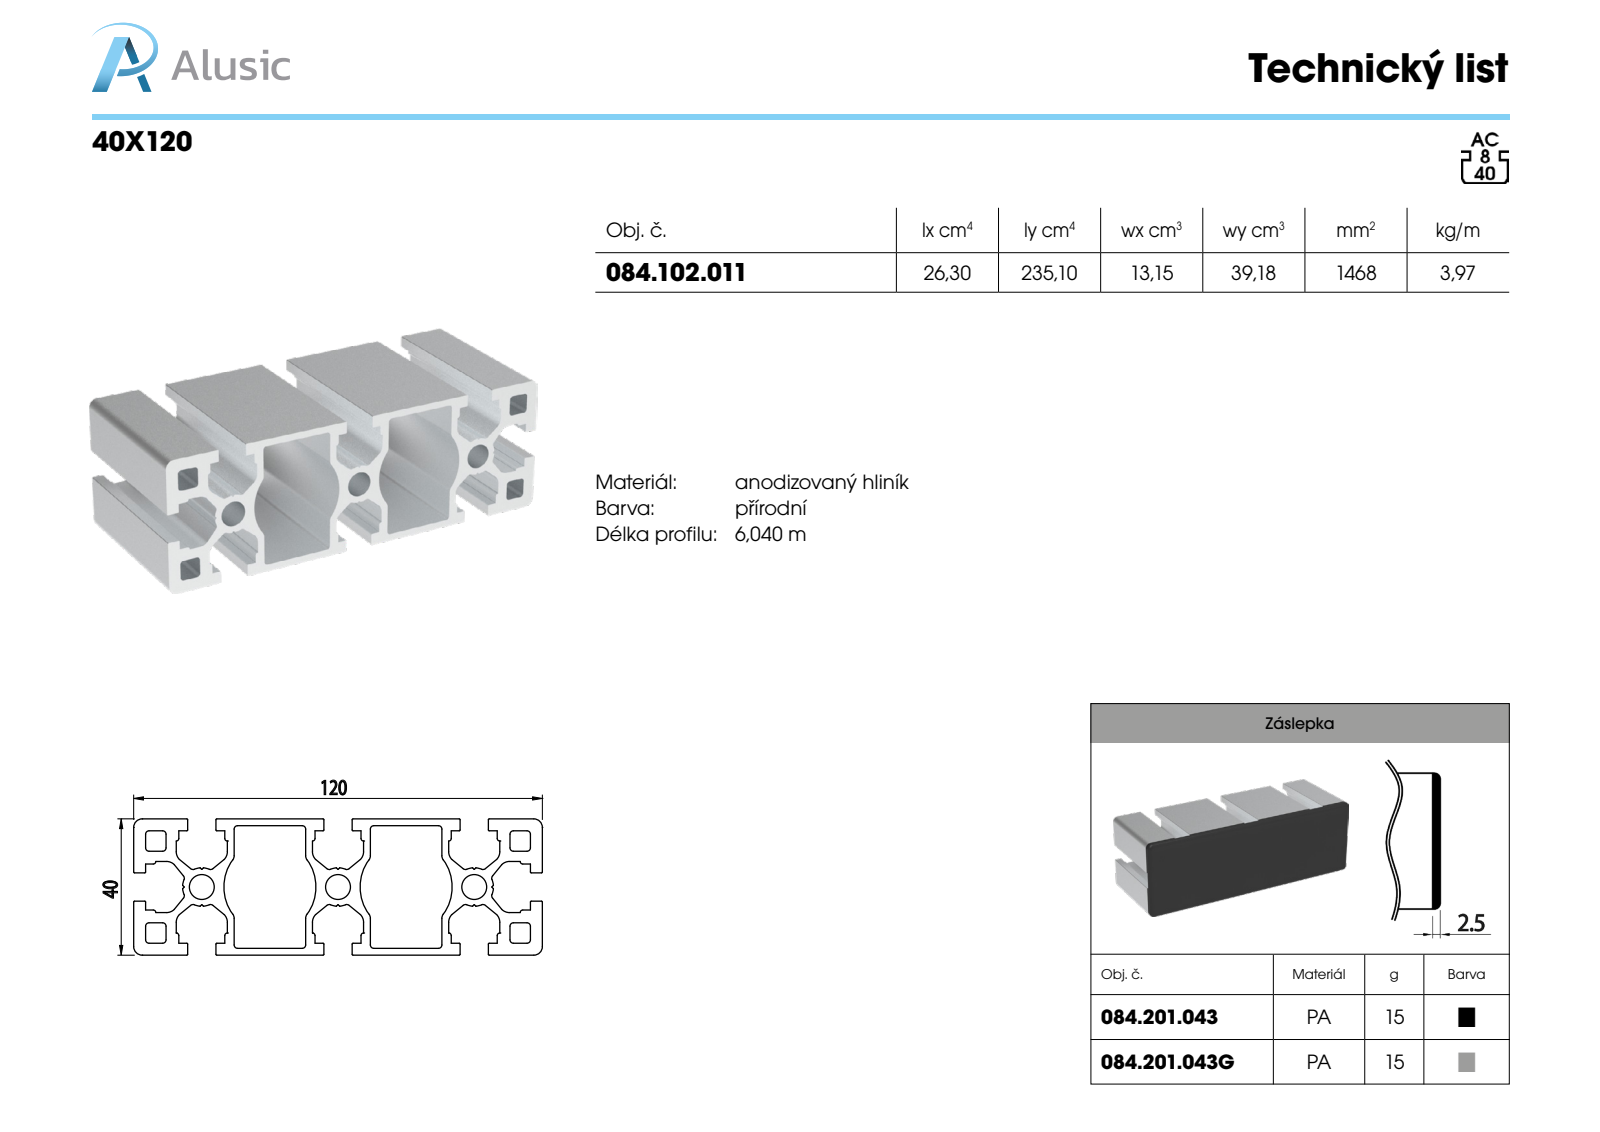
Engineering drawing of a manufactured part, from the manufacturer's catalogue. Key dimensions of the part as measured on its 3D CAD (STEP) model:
Part name (STEP PRODUCT): 084.102.011
STEP written by: SolidWorks 2016 (CONFIG_CONTROL_DESIGN)
Units: millimetres
Bodies: 1 solid, 319 faces (138 planar, 181 cylindrical, 0 other)
Overall size (bounding box): 120 × 100 × 40
Volume: 146 723 mm³ · Surface area: 103 123 mm²
Round holes (diameter × count): ⌀7.3 ×3
Partial cylindrical surfaces — rounded edges, fillets, slot ends (radius × count): R1 ×40, R0.25 ×32, R0.1 ×24, R0.75 ×16, R3.2 ×16, R2 ×8, R2.5 ×4, R5.65 ×3
Main face-to-face distances: 40, 38, 2, 3.5, 36.5, 1.5, 34.5, 21, 36, 3.35
Hole centre spacings: 40, 80
